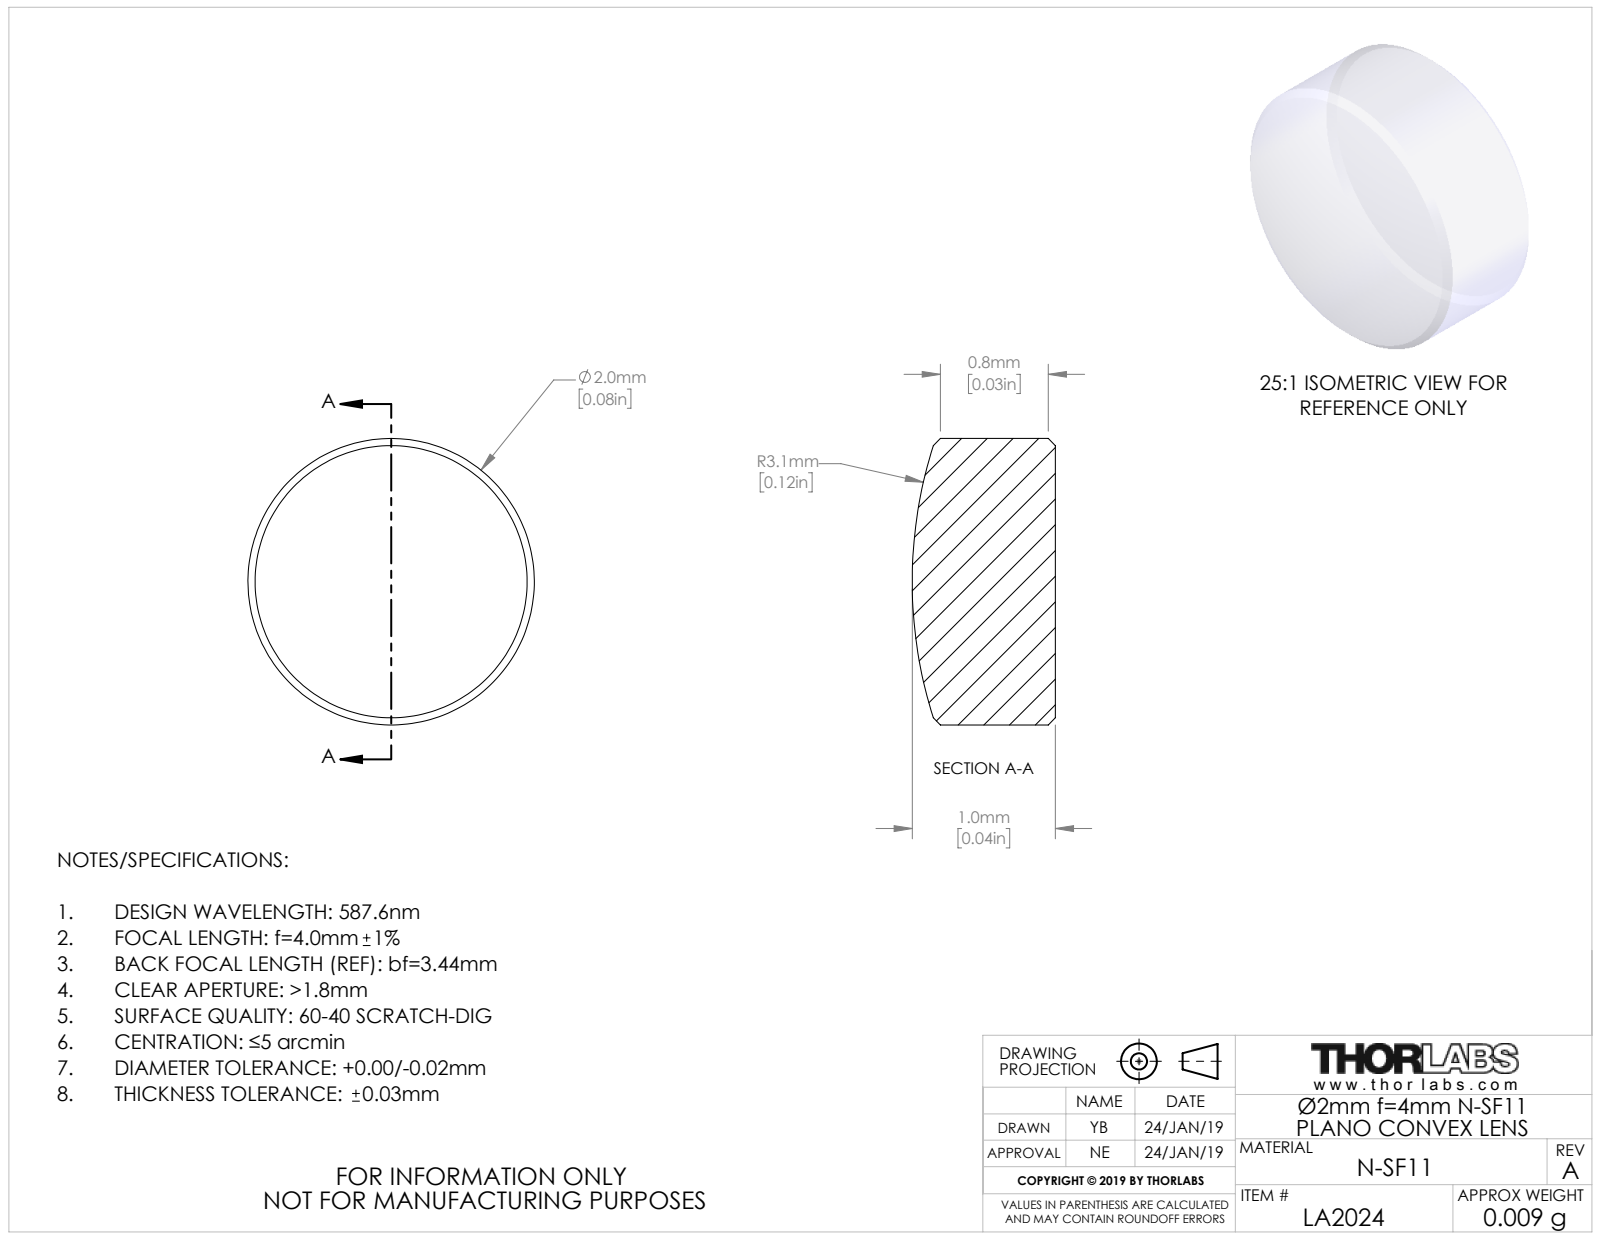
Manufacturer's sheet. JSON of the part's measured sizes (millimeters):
{"part_name": "TTN162739-E0W", "step_written_by": "SolidWorks 2018 (CONFIG_CONTROL_DESIGN)", "units": "millimeters", "bodies": {"solids": 1, "faces": 9, "planar": 1, "cylindrical": 2, "other": 6}, "overall_size": [2, 2, 1], "volume_mm3": 3, "surface_area_mm2": 11, "round_bosses_or_shafts": [[2, 1]]}
